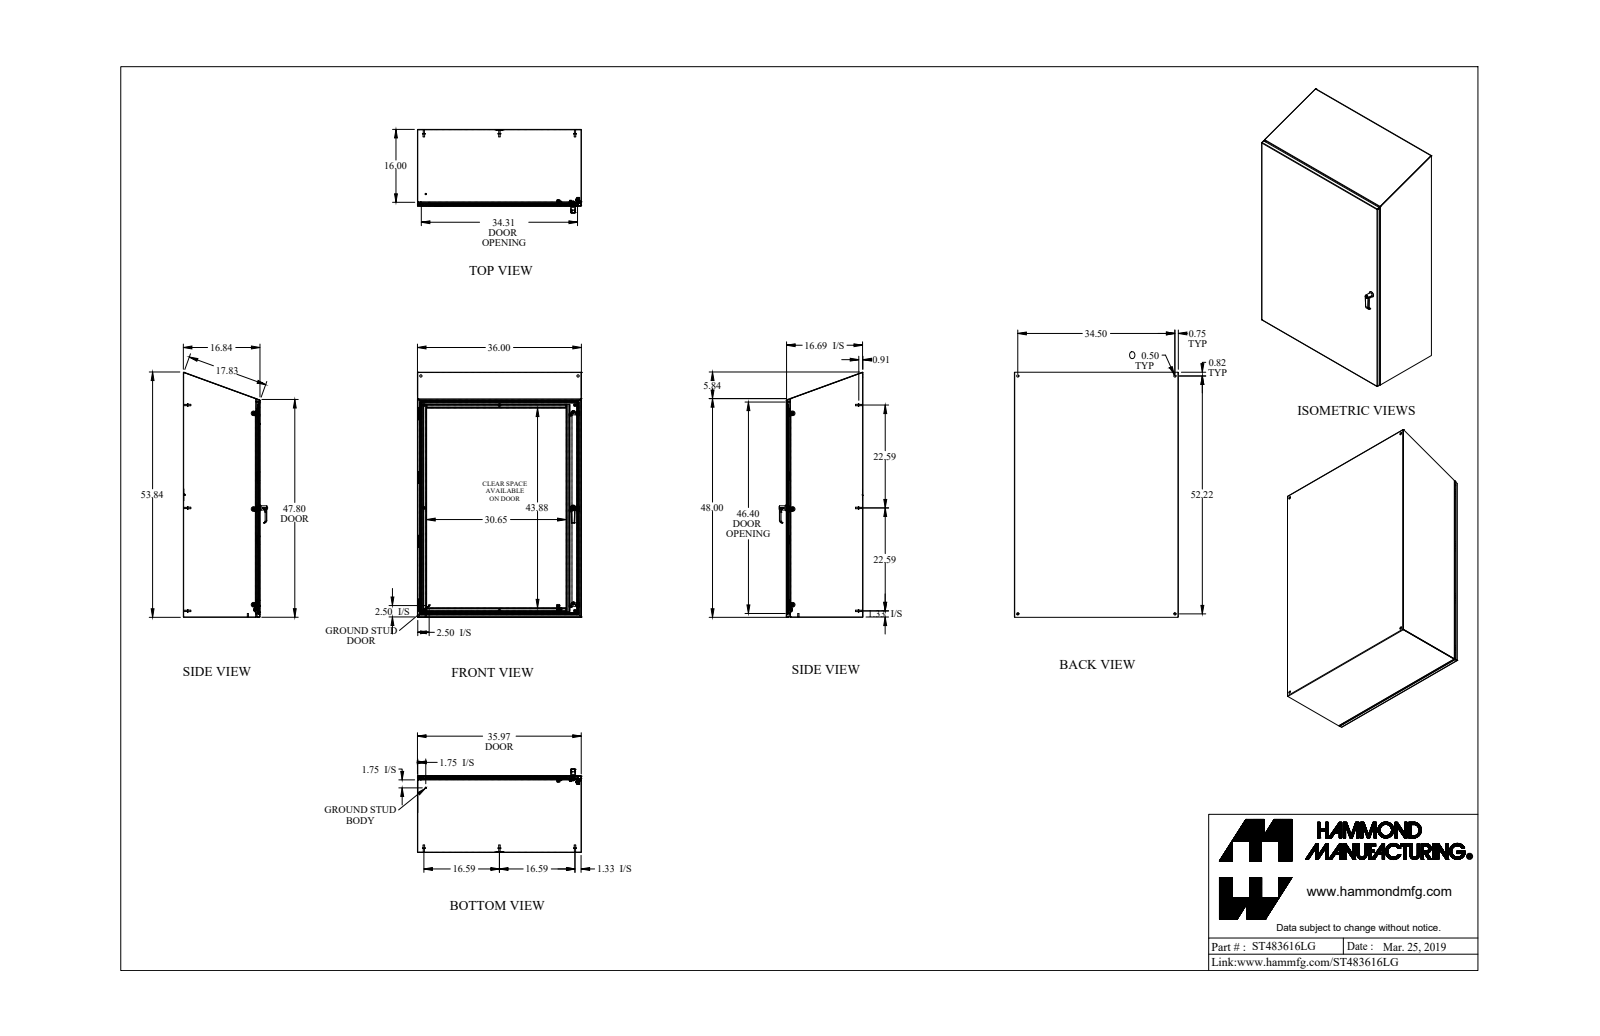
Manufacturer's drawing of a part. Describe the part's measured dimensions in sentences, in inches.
The part is named "ST483616LG". Its 3-D file was written by "SolidWorks 2018 (AUTOMOTIVE_DESIGN)". It is 64 solids with 1731 faces: 765 planar, 643 cylindrical and 323 other. Overall it measures 53.791 by 36 by 18.367 inches. Its volume is 526.5 cubic inches and its surface area 14 725 square inches. Round holes: 6 of diameter 0.176, 4 of diameter 0.196, 4 of diameter 0.5, 3 of diameter 0.25, 3 of diameter 0.265, 3 of diameter 0.413, 2 of diameter 0.256, 2 of diameter 0.313, 2 of diameter 0.394, 1 of diameter 0.172, 1 of diameter 0.24, 1 of diameter 0.242. Round bosses or shafts: 9 of diameter 0.313, 9 of diameter 0.27, 7 of diameter 0.625, 7 of diameter 0.25, 6 of diameter 0.375, 6 of diameter 0.156, 3 of diameter 1, 3 of diameter 0.625. Partial cylindrical surfaces (rounded edges, fillets, slot ends): 24 of radius 0.043, 24 of radius 0.081, 19 of radius 0.036, 18 of radius 0.108, 17 of radius 0.062, 15 of radius 0.03, 10 of radius 0.094, 9 of radius 0.016. The main face-to-face distances are 0.072, 16.765, 16.693, 16.837, 35.928, 35.856, 36, 15.928, 0.837, 0.038. The hole center spacings are 21, 42, 0.787, 34.5, 52.219, 62.586, 0.786, 2.359.
